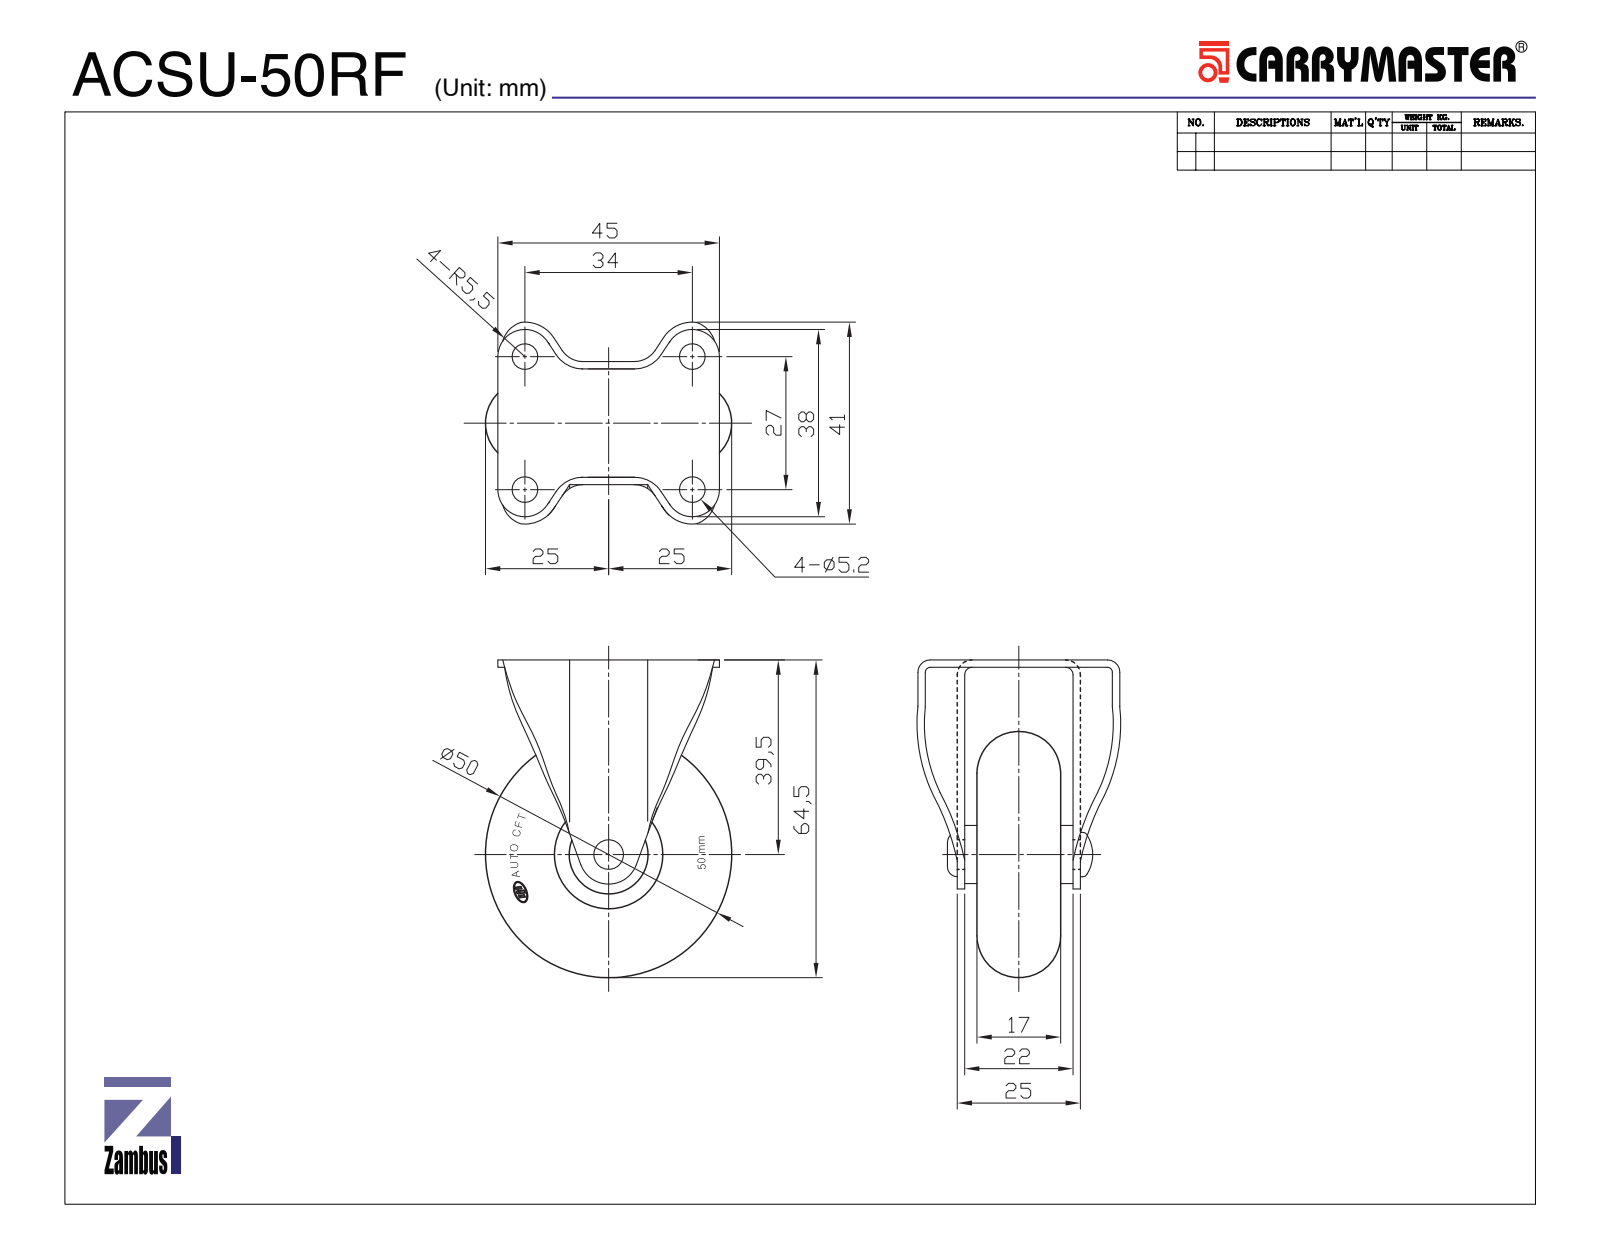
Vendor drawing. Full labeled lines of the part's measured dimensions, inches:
Part name (STEP PRODUCT): ACSU-50RF
STEP written by: SolidWorks 2015 (CONFIG_CONTROL_DESIGN)
Units: inches
Bodies: 10 solids, 321 faces (70 planar, 157 cylindrical, 94 other)
Overall size (bounding box): 2.539 × 1.969 × 1.614
Volume: 2.18 in³ · Surface area: 34.52 in²
Round holes (diameter × count): ⌀0.205 ×4, ⌀0.236 ×1, ⌀0.24 ×1, ⌀0.315 ×1, ⌀0.407 ×1, ⌀0.512 ×1, ⌀0.541 ×1, ⌀0.63 ×1, ⌀0.866 ×1
Round bosses / shafts (diameter × count): ⌀1.142 ×1, ⌀0.63 ×1, ⌀0.413 ×1, ⌀0.404 ×1, ⌀0.354 ×1
Partial cylindrical surfaces — rounded edges, fillets, slot ends (radius × count): R0.039 ×32, R0.167 ×4, R0.197 ×4, R0.217 ×4, R0.256 ×4, R0.28 ×4, R0.236 ×1, R0.531 ×1
Main face-to-face distances: 0.059, 0.669, 0.768, 0.157, 0.827, 0.925, 0.098, 0.984, 0.866, 0.036
Hole centre spacings: 1.063, 1.339, 1.709
